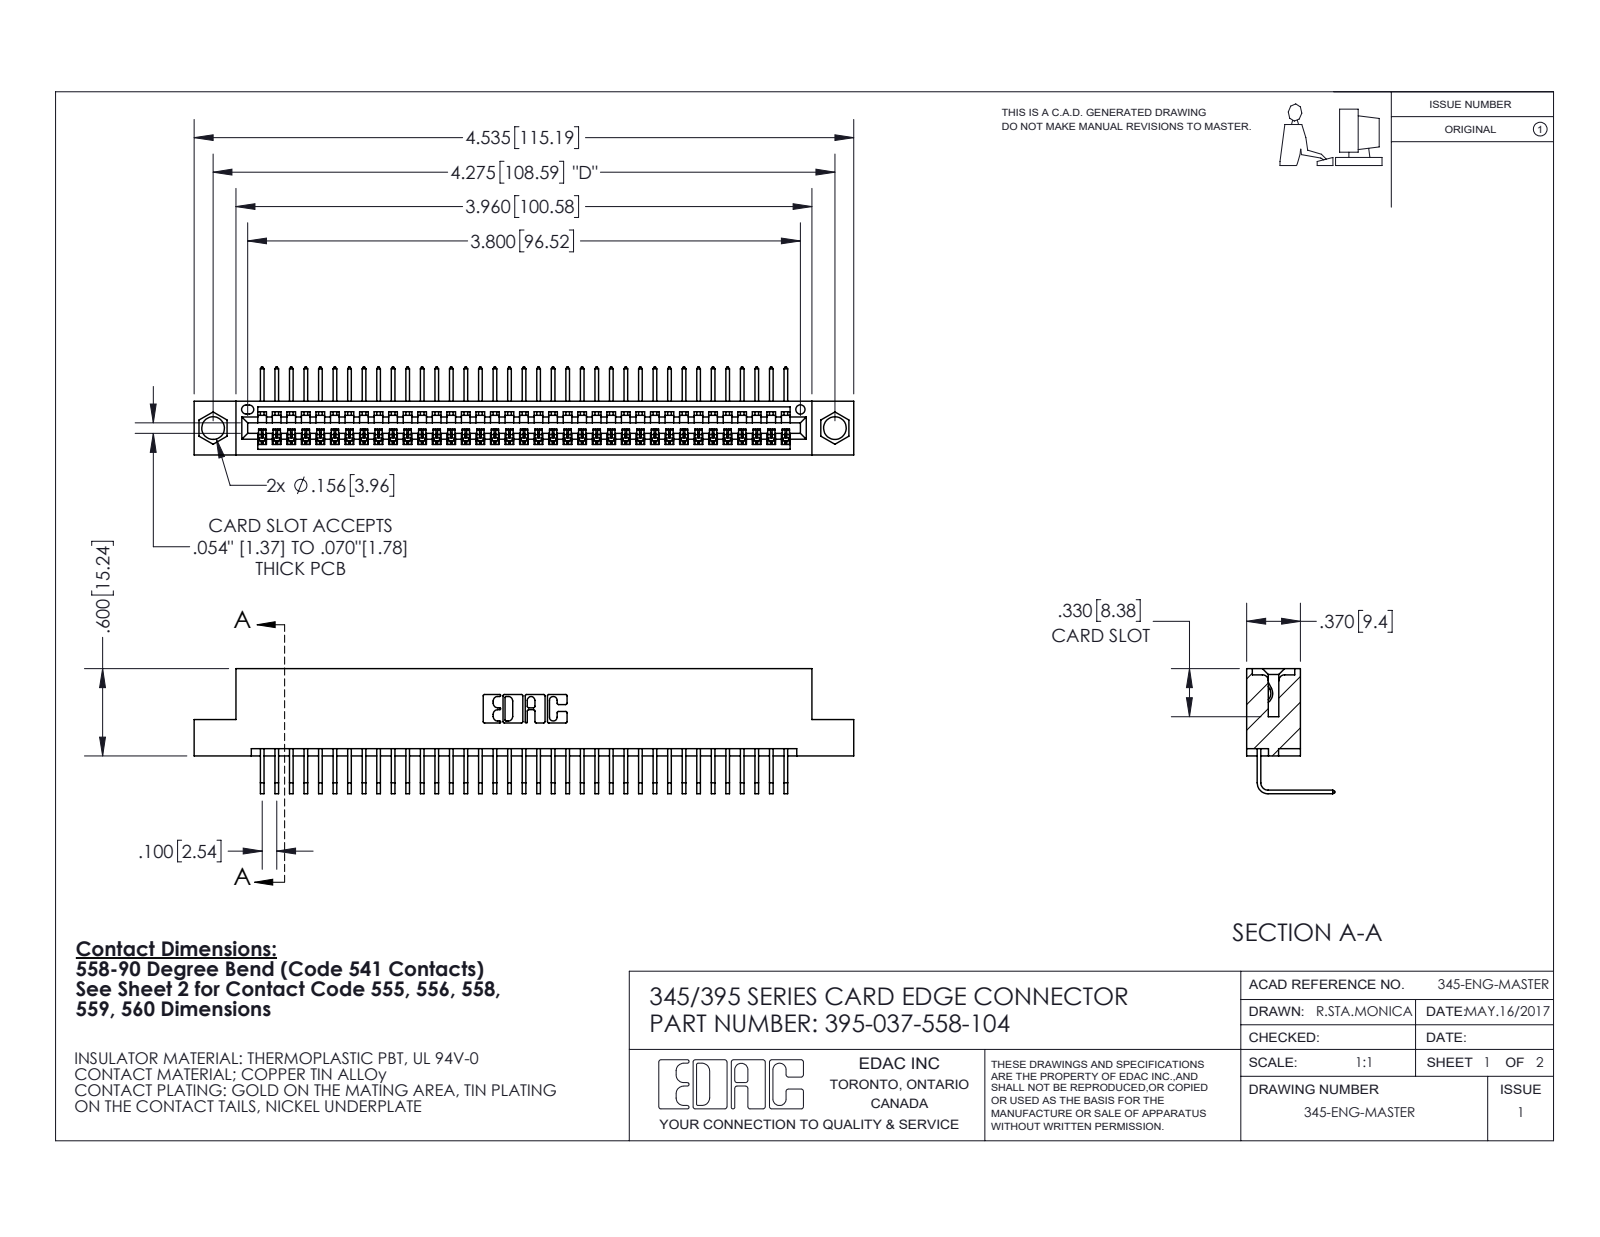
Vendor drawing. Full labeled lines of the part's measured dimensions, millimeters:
Part name (STEP PRODUCT): 395-037-558-104; 345 Part_Flush Mounting Lugs - 0.156 Dia-TI; 345-292-001_558 Tail - 2
STEP written by: SolidWorks 2020 (CONFIG_CONTROL_DESIGN)
Units: millimetres
Bodies: 38 solids, 2360 faces (1648 planar, 712 cylindrical, 0 other)
Overall size (bounding box): 115.2 × 21.8 × 15.4
Volume: 10 900 mm³ · Surface area: 15 010 mm²
Round holes (diameter × count): ⌀4 ×2, ⌀1.6 ×1
Partial cylindrical surfaces — rounded edges, fillets, slot ends (radius × count): R0.2 ×74, R0.3 ×22, R0.2 ×6, R0.8 ×6, R0.7 ×3, R0.8 ×2, R1 ×2, R0.4 ×1
Main face-to-face distances: 1.8, 7.6, 9.4, 5.1, 2.5, 6.9, 0.6, 5.7, 3.8, 1.8
Hole centre spacings: 6.9, 102.6, 108.6
